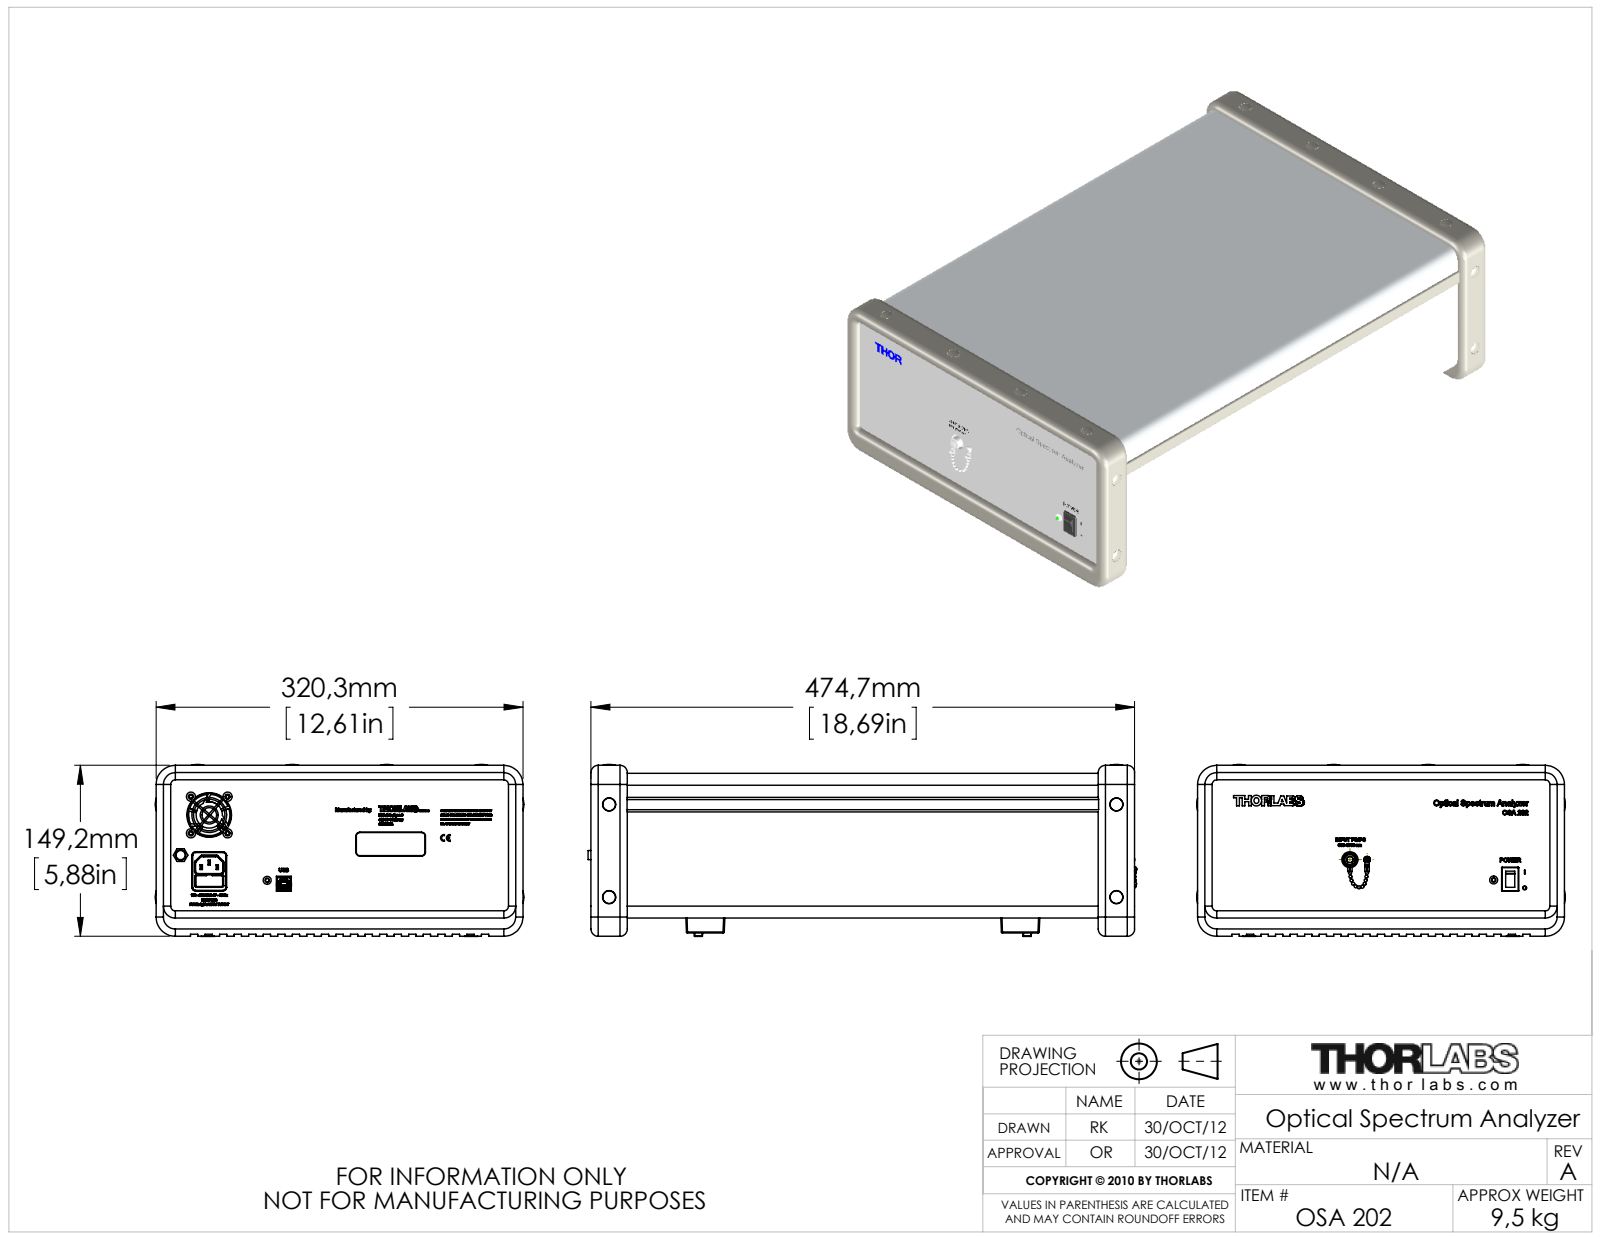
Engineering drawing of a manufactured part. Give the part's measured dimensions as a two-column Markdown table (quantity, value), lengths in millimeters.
| quantity | value |
| --- | --- |
| part name | STN012077 |
| STEP written by | SolidWorks 2012 (AUTOMOTIVE_DESIGN) |
| units | millimeters |
| bodies | 104 solids, 11706 faces (4111 planar, 4331 cylindrical, 3264 other) |
| overall size | 479.31 × 321.82 × 150.11 |
| volume | 1 895 000 mm³ |
| surface area | 1 533 000 mm² |
| round holes (diameter × count) | 2 × 704, 4.27 × 14, 5.08 × 12, 11.43 × 12, 3.1 × 8, 3.24 × 8, 4 × 8, 4.22 × 8, 5.41 × 8, 10.16 × 8, 2.5 × 6, 2.26 × 4 |
| round bosses / shafts (diameter × count) | 4 × 18, 3 × 15, 11.05 × 13, 1.5 × 11, 11.05 × 9, 5.02 × 9, 7.9 × 8, 6.51 × 8 |
| partial cylindrical surfaces (radius × count) | 0.5 × 127, 0.2 × 84, 0.3 × 80, 1 × 64, 1.5 × 29, 0.27 × 24, 0.91 × 24, 6.35 × 18 |
| main face-to-face distances | 1, 125.4, 124.4, 126.4, 306.6, 460.8, 81, 44.4, 307.6, 305.6 |
| hole center spacings | 11.18, 5, 15.81, 7.07, 10, 18.03, 15, 20.62 |
